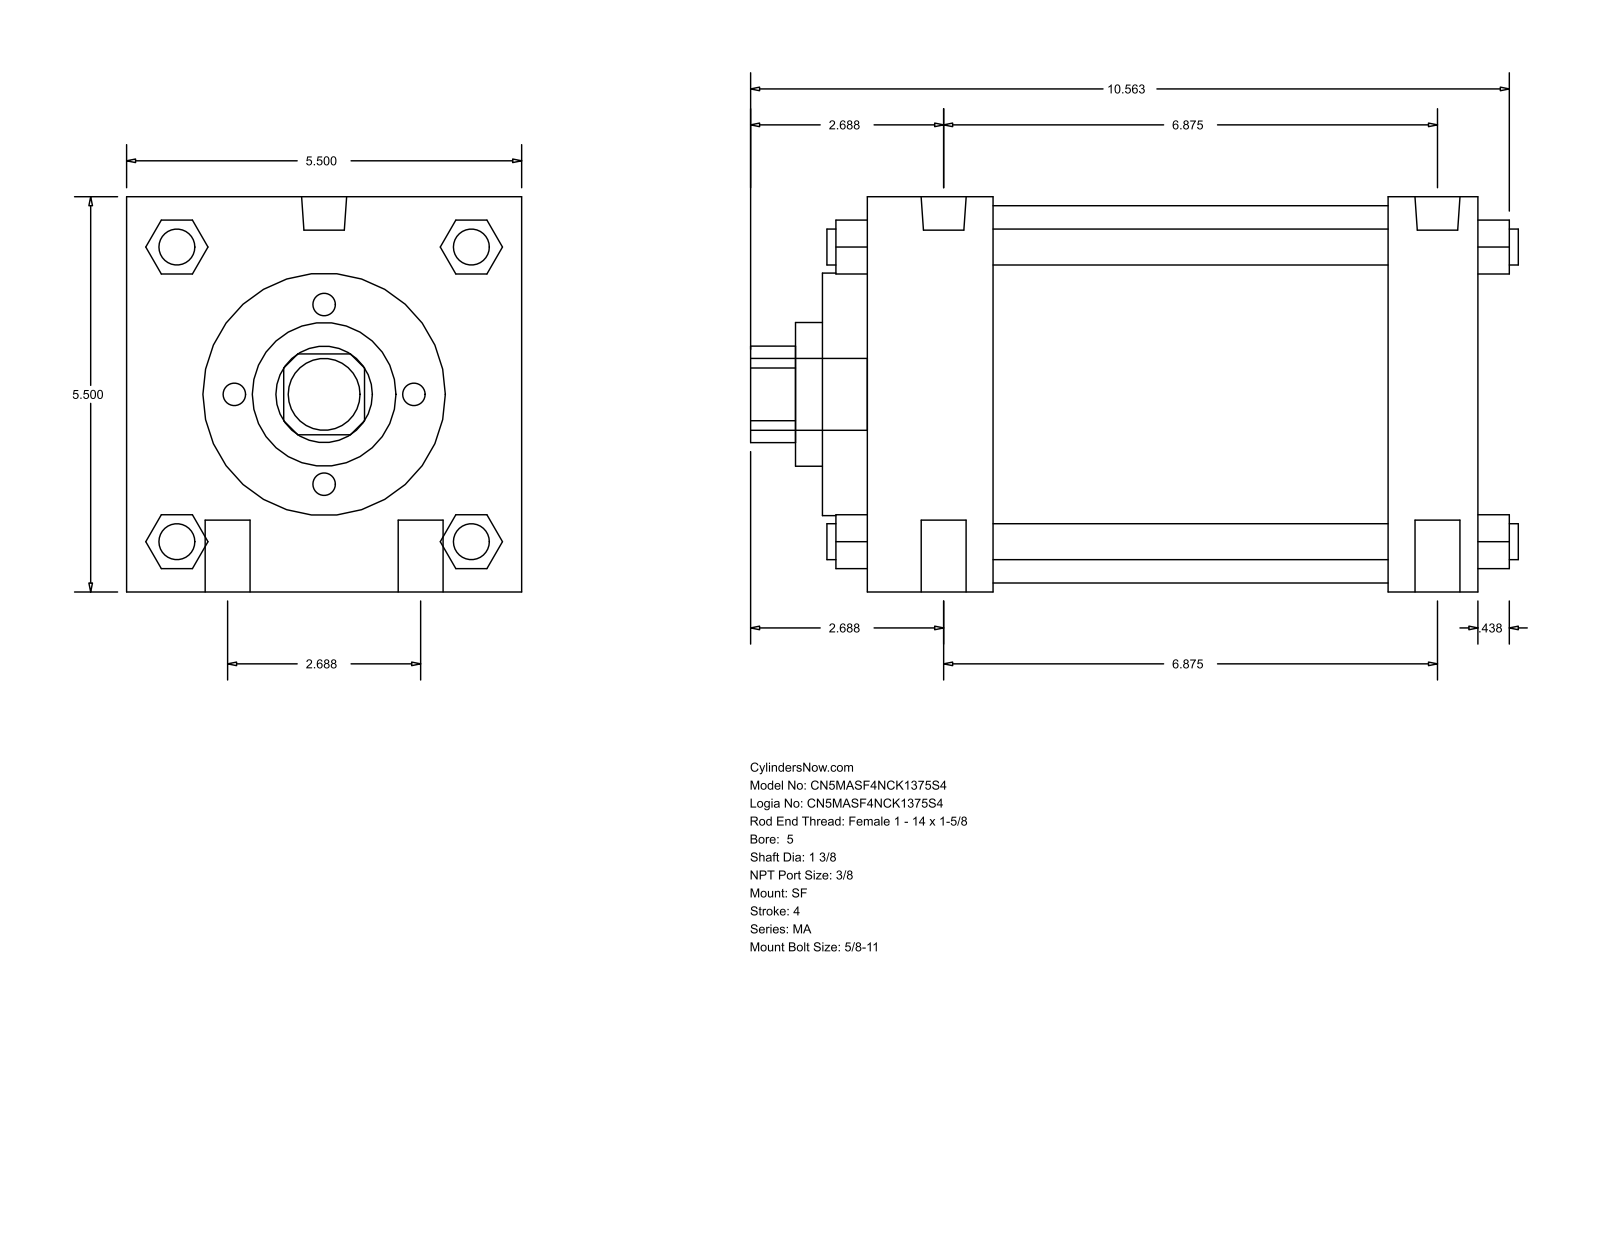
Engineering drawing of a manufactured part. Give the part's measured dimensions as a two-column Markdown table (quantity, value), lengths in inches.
| quantity | value |
| --- | --- |
| part name | MA_SF__0500_1.375 |
| STEP written by | GSSL Pune (CONFIG_CONTROL_DESIGN) |
| units | inches |
| bodies | 0 solids, 126 faces (95 planar, 31 cylindrical, 0 other) |
| overall size | 10.687 × 5.5 × 5.5 |
| round holes (diameter × count) | 1.375 × 1, 2 × 1, 3.375 × 1, 5.25 × 1 |
| round bosses / shafts (diameter × count) | 0.625 × 4, 0.5 × 4, 0.627 × 2, 0.437 × 2, 1 × 1 |
| partial cylindrical surfaces (radius × count) | 0.672 × 1 |
| main face-to-face distances | 5.5, 8.5, 1.75, 7.25, 5.5, 6.75, 1.25, 0.625, 2.375, 7.875 |
